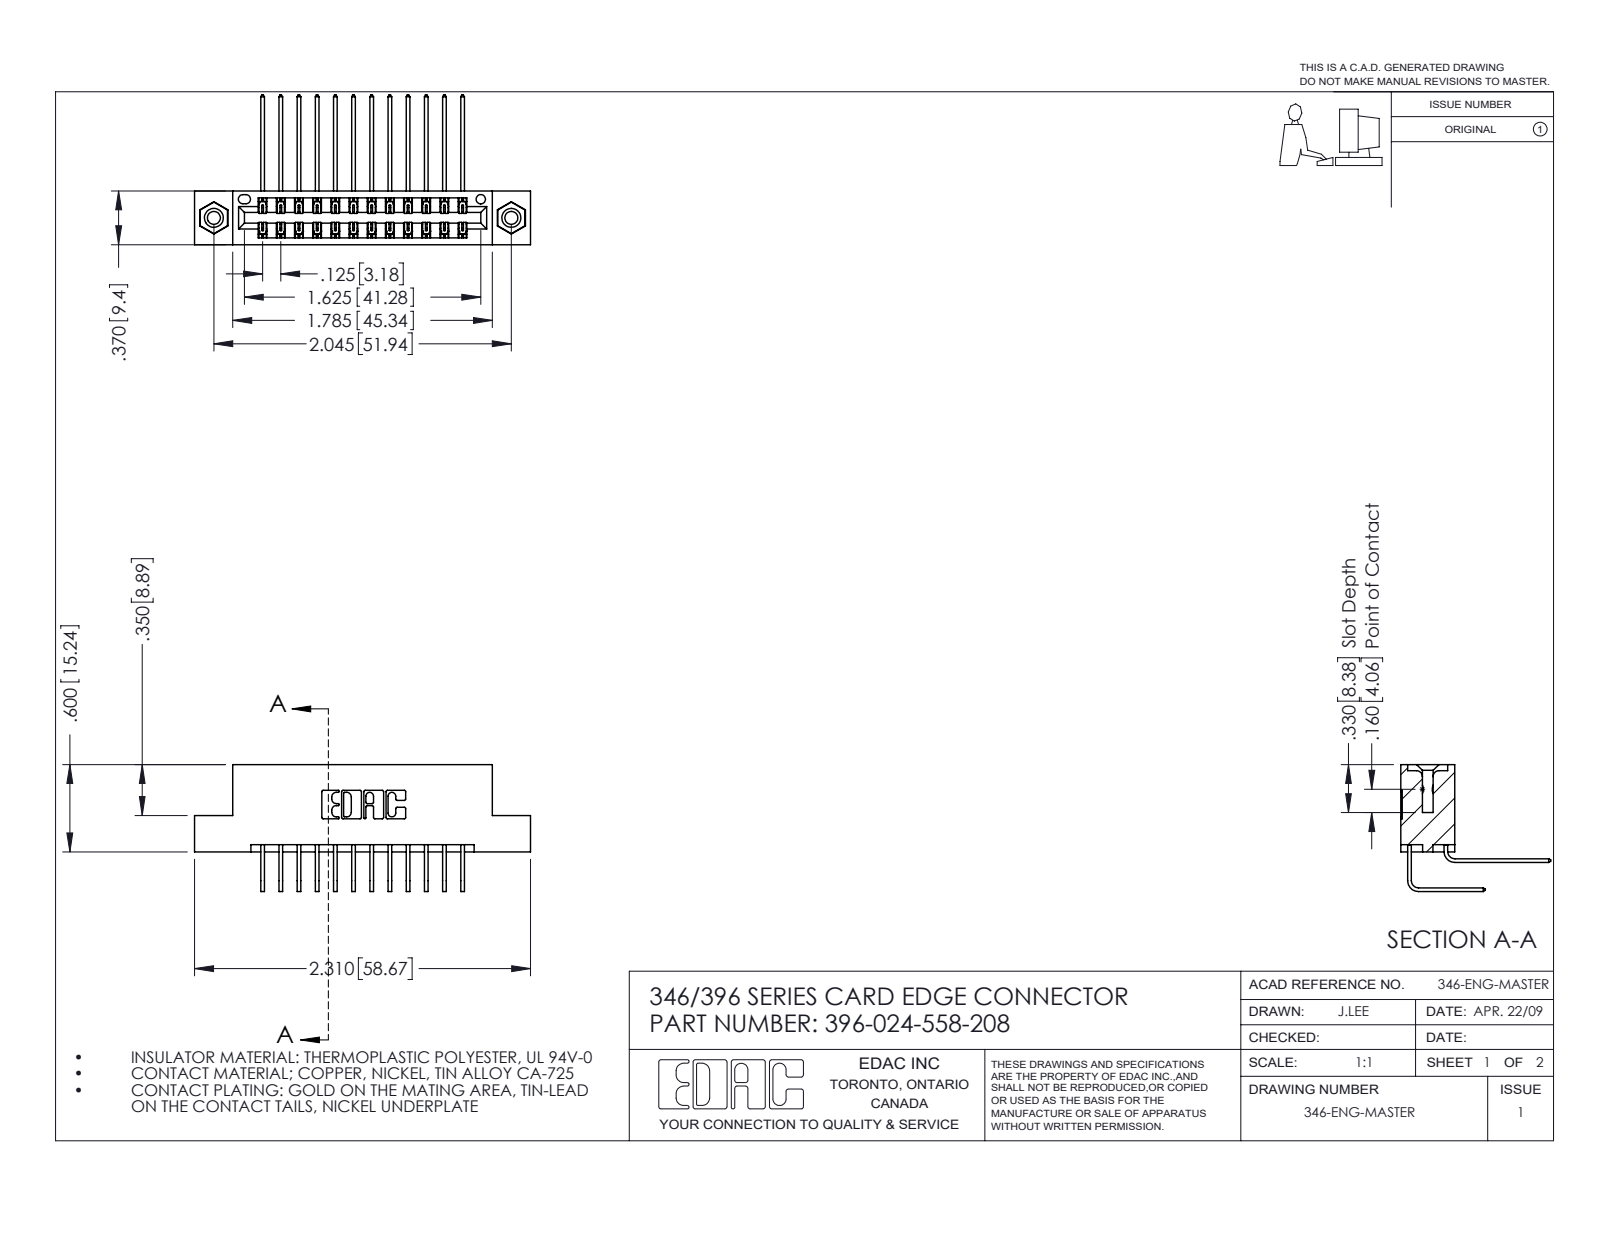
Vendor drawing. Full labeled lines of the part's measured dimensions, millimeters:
Part name (STEP PRODUCT): 345-292-001_558 559 Tail - 1; 396-024-558-208; 346 Part_Flush Mounting Lugs - 0.156 Dia-TI; 345-250-001_345-250-003-102 (+1 more)
STEP written by: SolidWorks 2016 (CONFIG_CONTROL_DESIGN)
Units: millimetres
Bodies: 27 solids, 1478 faces (996 planar, 466 cylindrical, 16 other)
Overall size (bounding box): 58.7 × 26.2 × 22.2
Volume: 5 620 mm³ · Surface area: 7 935 mm²
Round holes (diameter × count): ⌀2.3 ×2, ⌀3.2 ×2, ⌀4 ×2, ⌀1.6 ×1
Round bosses / shafts (diameter × count): ⌀3.9 ×2
Partial cylindrical surfaces — rounded edges, fillets, slot ends (radius × count): R0.2 ×36, R0.3 ×22, R0.2 ×6, R0.8 ×6, R0.7 ×3, R0.4 ×2, R0.6 ×2, R0.6 ×2
Main face-to-face distances: 8.2, 1.2, 6.4, 9.4, 0.6, 7.6, 1.8, 7, 3.8, 5.6
Hole centre spacings: 6.2, 46.7, 51.9
